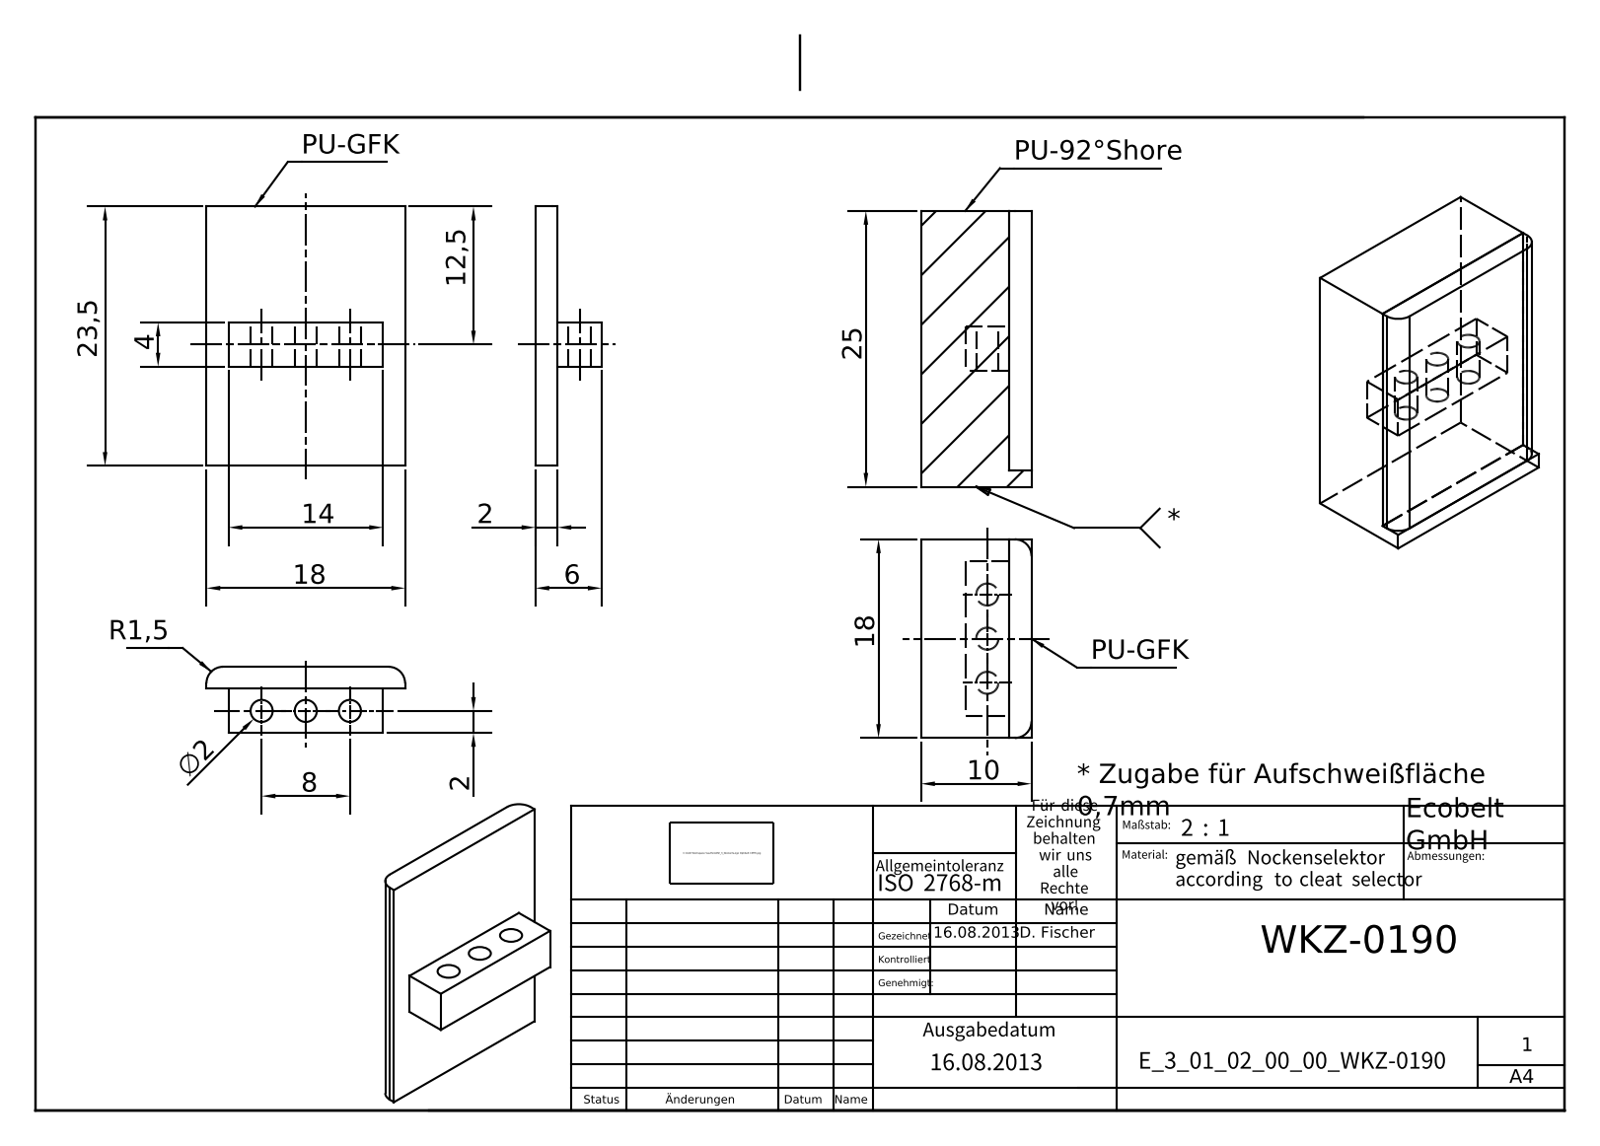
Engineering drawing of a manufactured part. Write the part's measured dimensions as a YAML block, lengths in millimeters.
part_name: "E_3_01_02_00_00_WKZ-0190; E_3_01_02_00_00_WKZ-0190_Teil1; E_3_01_02_00_00_WKZ-0190_Teil2"
step_written_by: "Autodesk Inventor 2025 (AUTOMOTIVE_DESIGN)"
units: millimeters
bodies: {solids: 2, faces: 24, planar: 19, cylindrical: 5, other: 0}
overall_size: [25, 18, 10]
volume: 4664
surface_area: 2846
round_holes:
  - {diameter: 2, count: 3}
partial_cylinders:
  - {radius: 1.5, count: 2}
face_to_face_distances: [8, 2, 10, 18, 25, 4, 10.5, 14.5, 1.5, 23.5]
hole_center_spacings: [4, 8]
